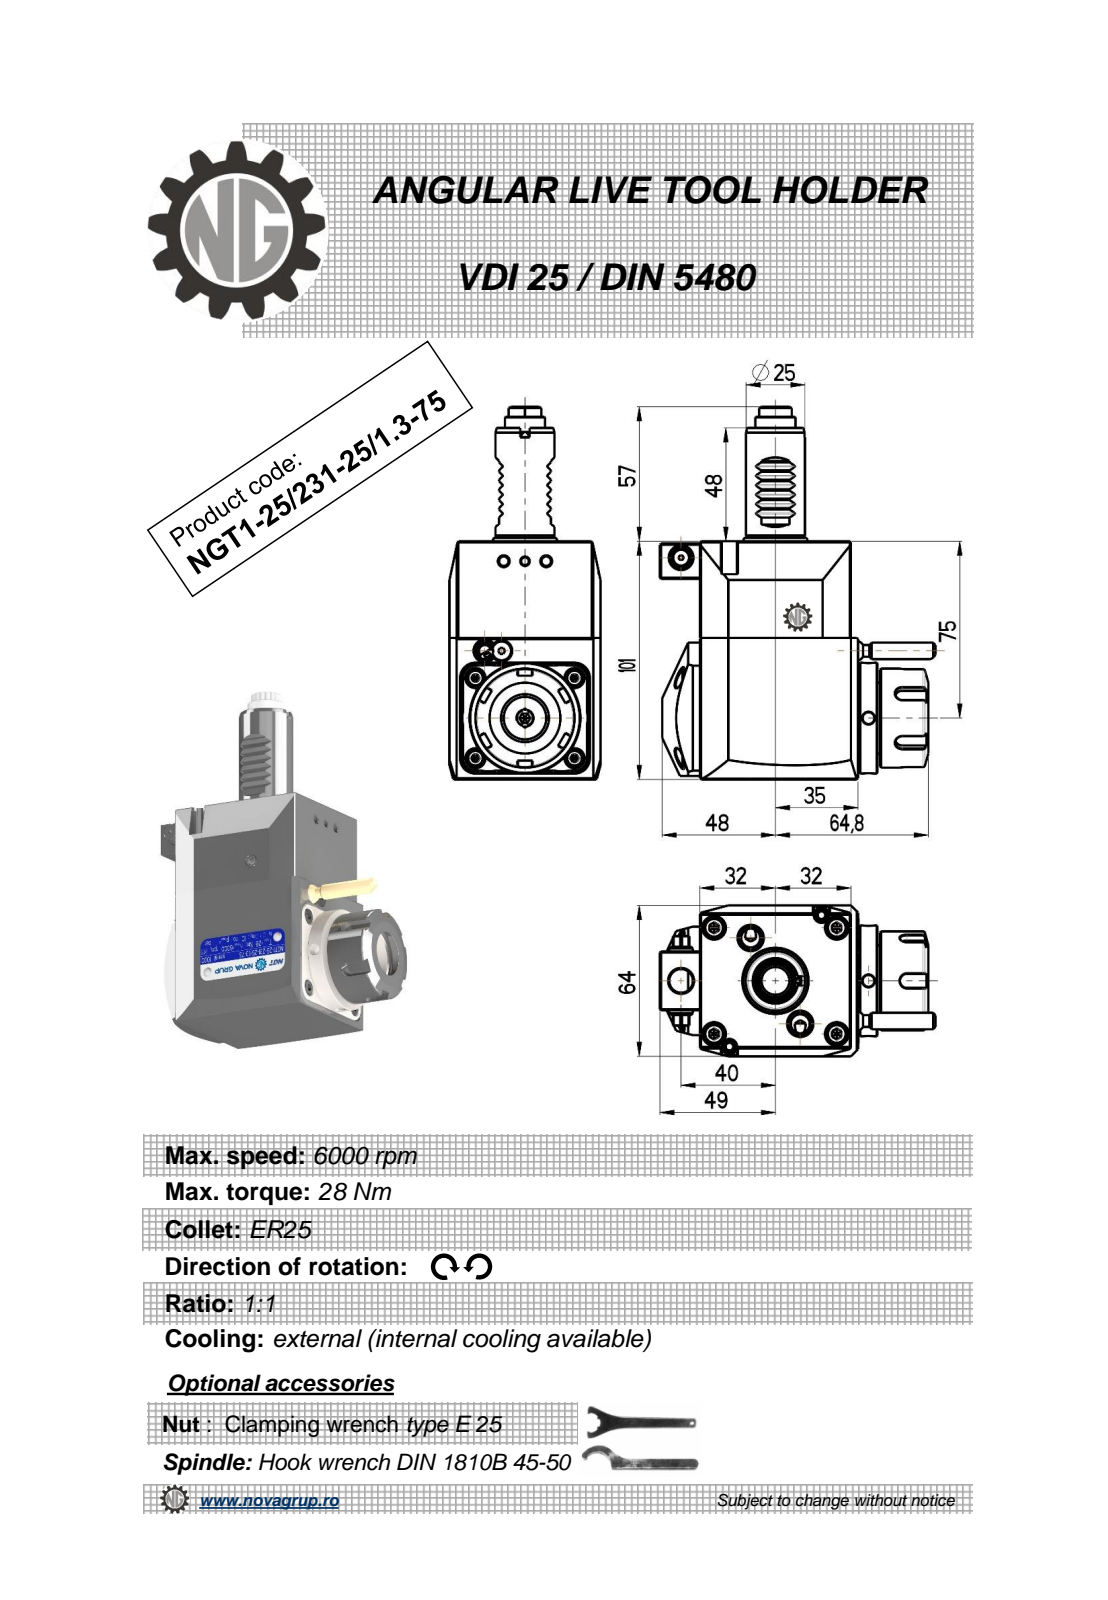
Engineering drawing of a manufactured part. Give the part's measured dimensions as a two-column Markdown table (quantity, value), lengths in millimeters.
| quantity | value |
| --- | --- |
| part name | NGT1_25_231_25_1_3_75 |
| STEP written by | PRO/ENGINEER BY PARAMETRIC TECHNOLOGY CORPORATION, 2010280 (CONFIG_CONTROL_DESIGN) |
| units | millimeters |
| bodies | 1 solid, 527 faces (199 planar, 157 cylindrical, 171 other) |
| overall size | 158 × 116.83 × 64 |
| volume | 511 599 mm³ |
| surface area | 49 634 mm² |
| round holes (diameter × count) | 5 × 2, 8.5 × 2, 2 × 1, 2.5 × 1, 3 × 1, 10 × 1, 20.3 × 1 |
| round bosses / shafts (diameter × count) | 7.96 × 2, 47 × 1, 42 × 1, 35 × 1, 33 × 1, 25 × 1, 17 × 1, 10 × 1 |
| partial cylindrical surfaces (radius × count) | 1.9 × 32, 0.3 × 12, 3 × 5, 3.5 × 4, 3.85 × 1, 6.08 × 1, 6.92 × 1, 10.5 × 1 |
| main face-to-face distances | 64, 101, 67.2, 3.2, 8, 3, 67, 7.5, 75.2, 11.2 |
| hole center spacings | 33.19, 41.63, 66.5, 79.45, 104.58 |
